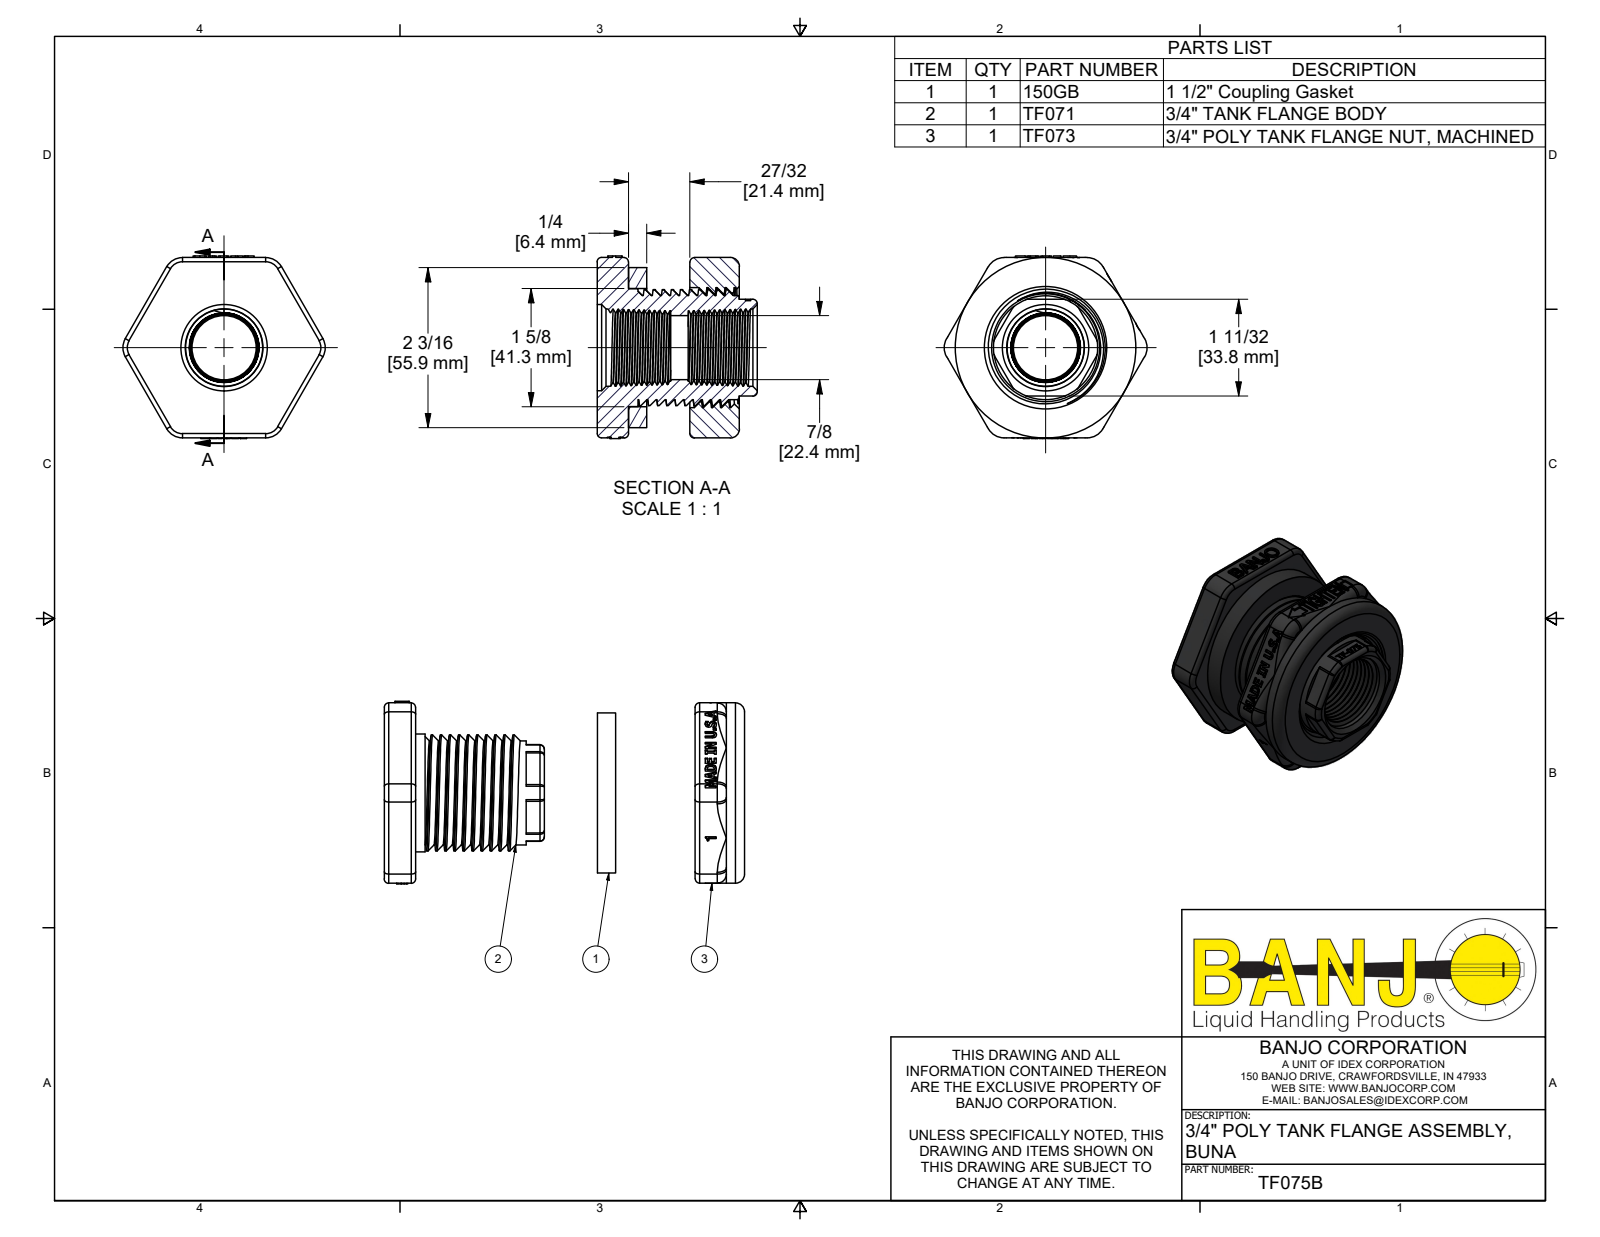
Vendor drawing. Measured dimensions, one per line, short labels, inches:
name: TF075B; TF071; TF073; TF073X (+1 more)
written by: Autodesk Inventor 2022 (AUTOMOTIVE_DESIGN)
unit: in
bodies: 3 solids, 863 faces (504 planar, 103 cylindrical, 256 other)
size: 2.786 × 2.51 × 2.2
volume: 6.205 in³; area: 59.91 in²
holes: 1× ⌀0.88, 1× ⌀1.185, 1× ⌀1.484, 1× ⌀1.625, 1× ⌀1.65
bosses: 1× ⌀2.48, 1× ⌀2.2, 1× ⌀1.62, 1× ⌀1.596, 1× ⌀1.43
rounds: 30× R0.06, 6× R0.062, 6× R0.125, 6× R0.25, 1× R0.316, 1× R0.44, 1× R0.495
face distances: 0.43, 1.274, 0.844, 0.25, 0.68, 0.594, 1.274, 1.954, 1.524, 0.68
